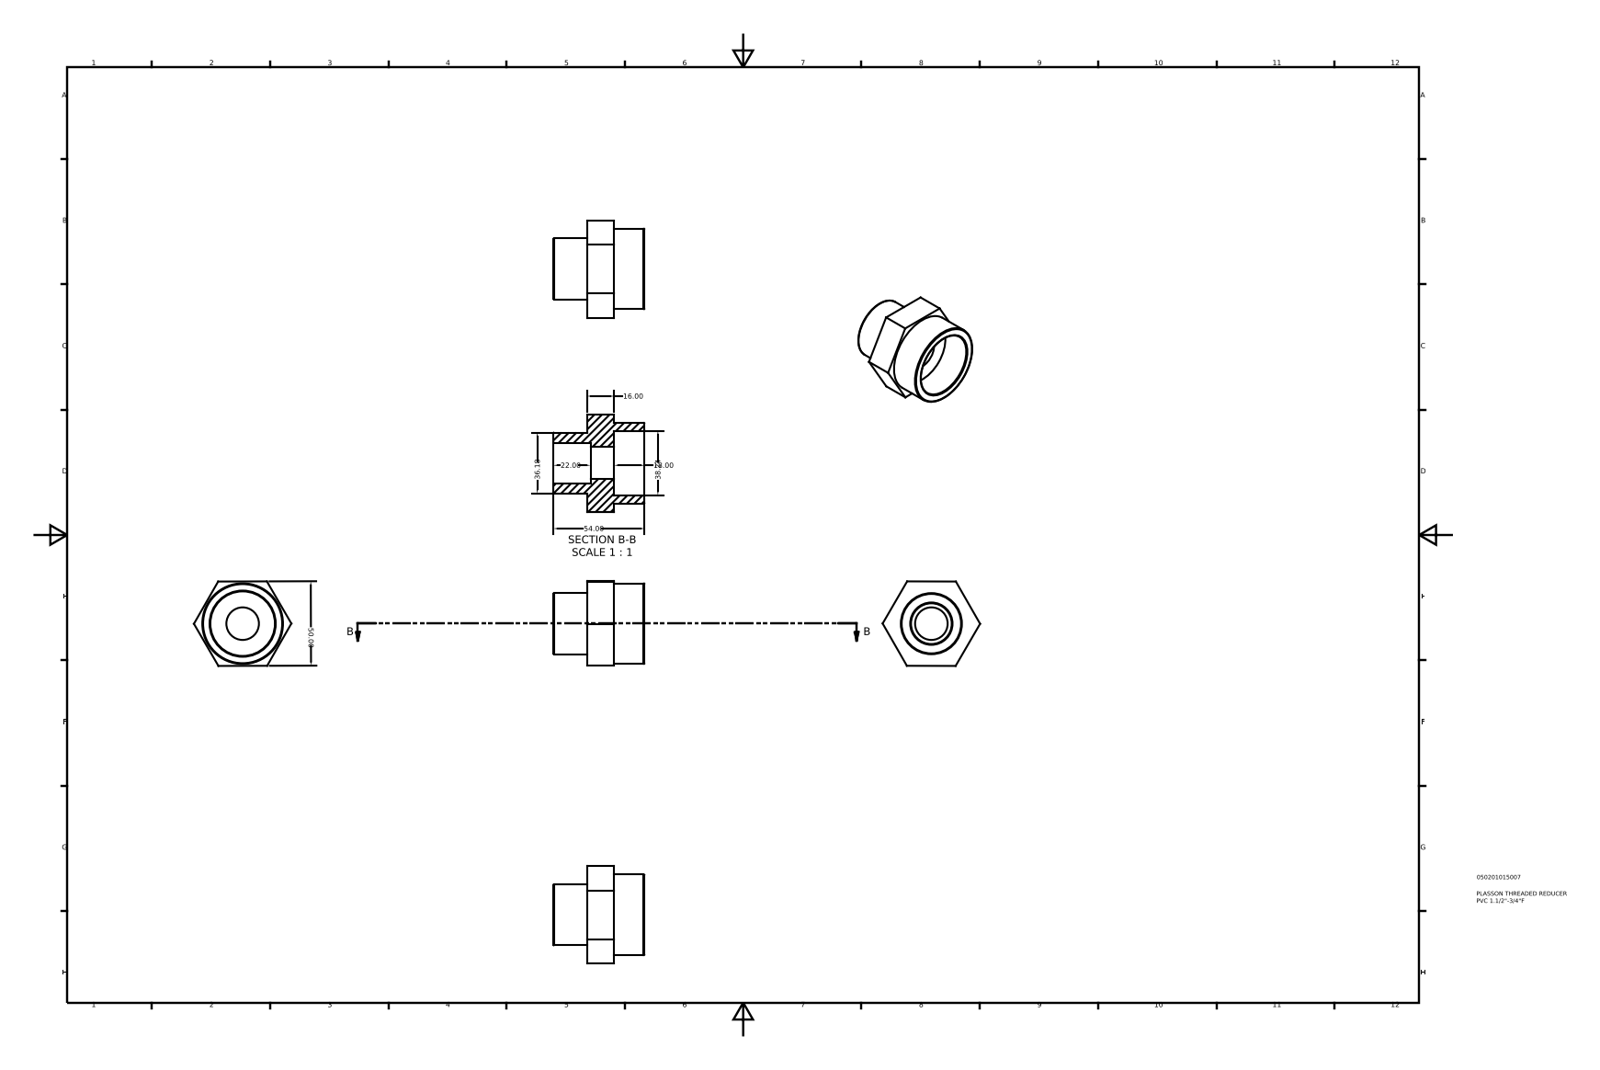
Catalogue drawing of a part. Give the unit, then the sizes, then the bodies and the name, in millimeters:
Units: millimetres
Overall size (bounding box): 57.73 × 54 × 50.09
Round holes (diameter × count): ⌀19.29 ×1, ⌀24.12 ×1, ⌀38.24 ×1
Round bosses / shafts (diameter × count): ⌀47.8 ×1, ⌀36.18 ×1
Main face-to-face distances: 16, 34, 18, 20, 36, 54, 50.04, 50.02, 50, 22
Volume: 52 662 mm³ · Surface area: 16 077 mm²
Bodies: 1 solid, 21 faces (12 planar, 5 cylindrical, 4 other)
Part name (STEP PRODUCT): 050201015007
STEP written by: Autodesk Inventor 2015 (AUTOMOTIVE_DESIGN)
